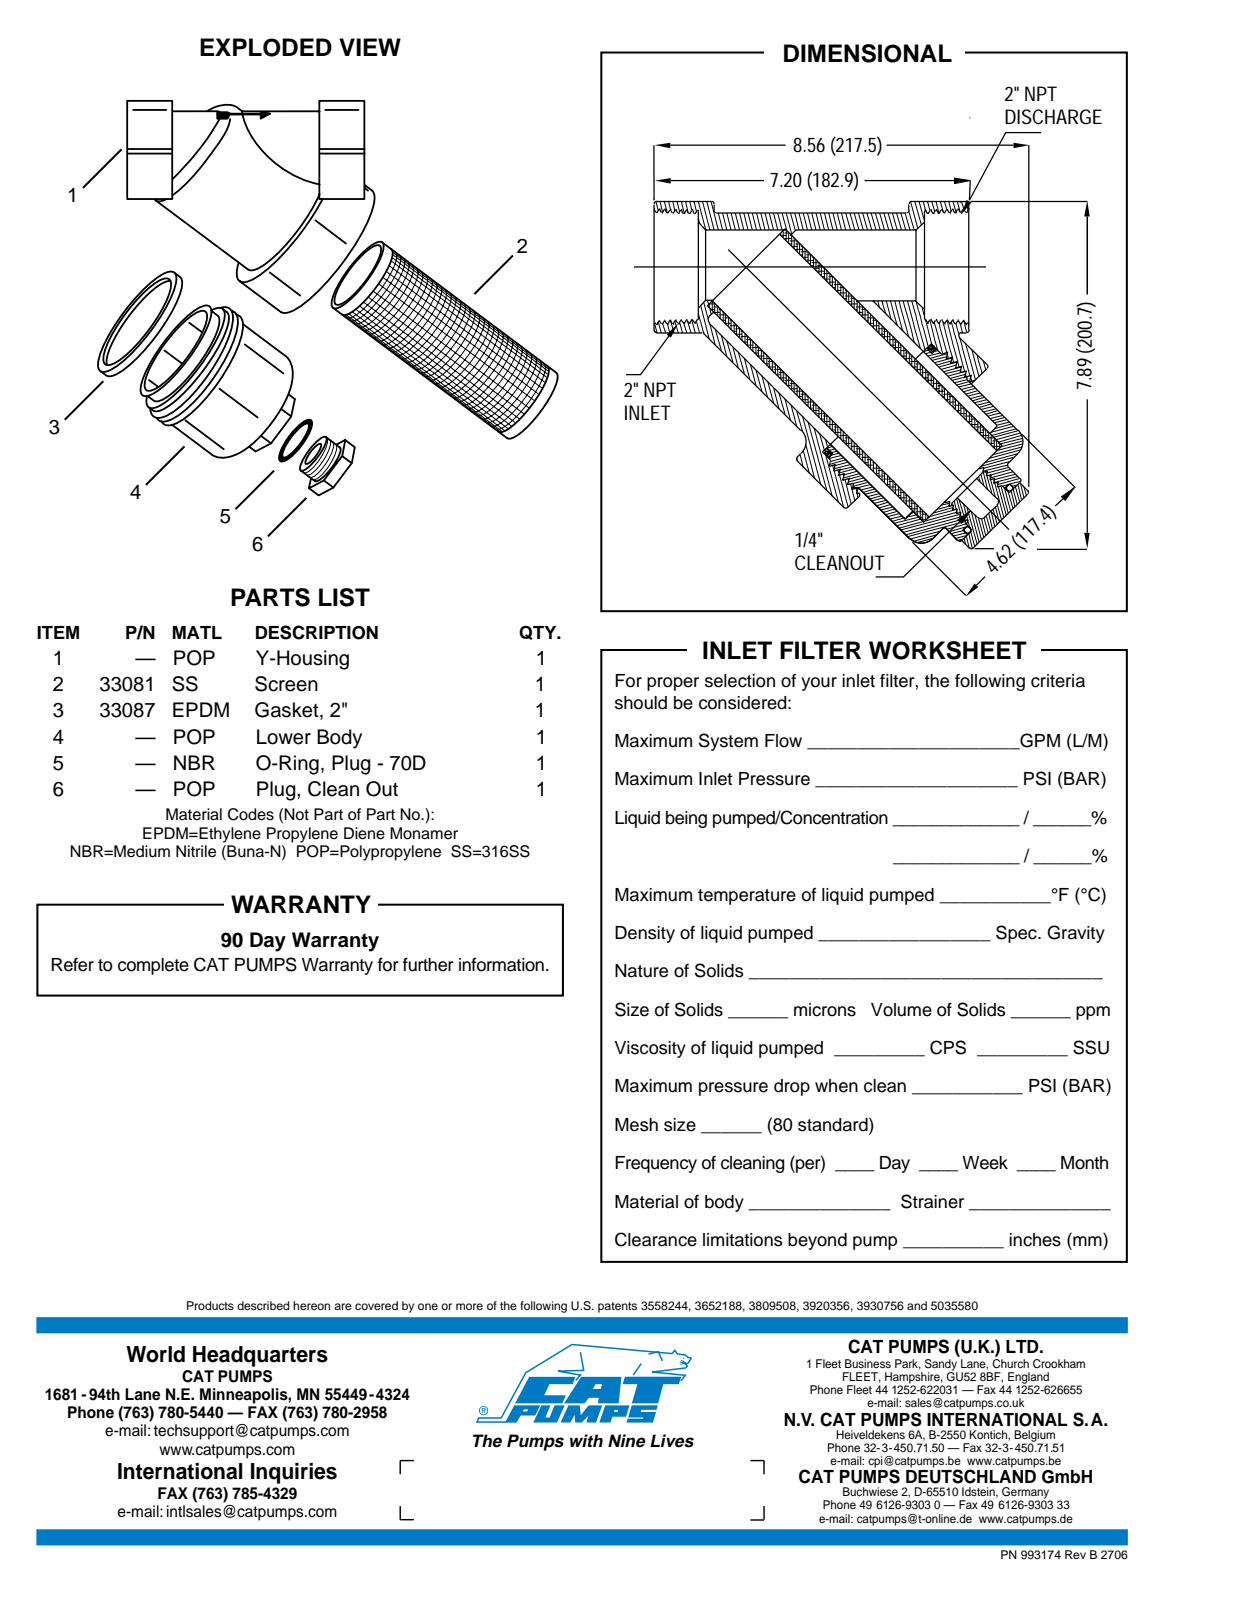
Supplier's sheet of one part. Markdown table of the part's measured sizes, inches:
| quantity | value |
| --- | --- |
| part name | 7109 |
| STEP written by | SolidWorks 2017 (CONFIG_CONTROL_DESIGN) |
| units | inches |
| bodies | 1 solid, 253 faces (47 planar, 84 cylindrical, 122 other) |
| overall size | 10.807 × 7.087 × 4.62 |
| volume | 109.6 in³ |
| surface area | 185.2 in² |
| round holes (diameter × count) | 2.188 × 2 |
| round bosses / shafts (diameter × count) | 4.62 × 1, 3.84 × 1, 3.66 × 1 |
| partial cylindrical surfaces (radius × count) | 0.1 × 22, 0.05 × 16, 0.107 × 6, 0.065 × 3, 1.492 × 2, 1.155 × 1 |
| main face-to-face distances | 1.8, 3.02, 1.44, 5.714, 0.85, 2.65, 7.154, 4.274, 1.635, 4.325 |
